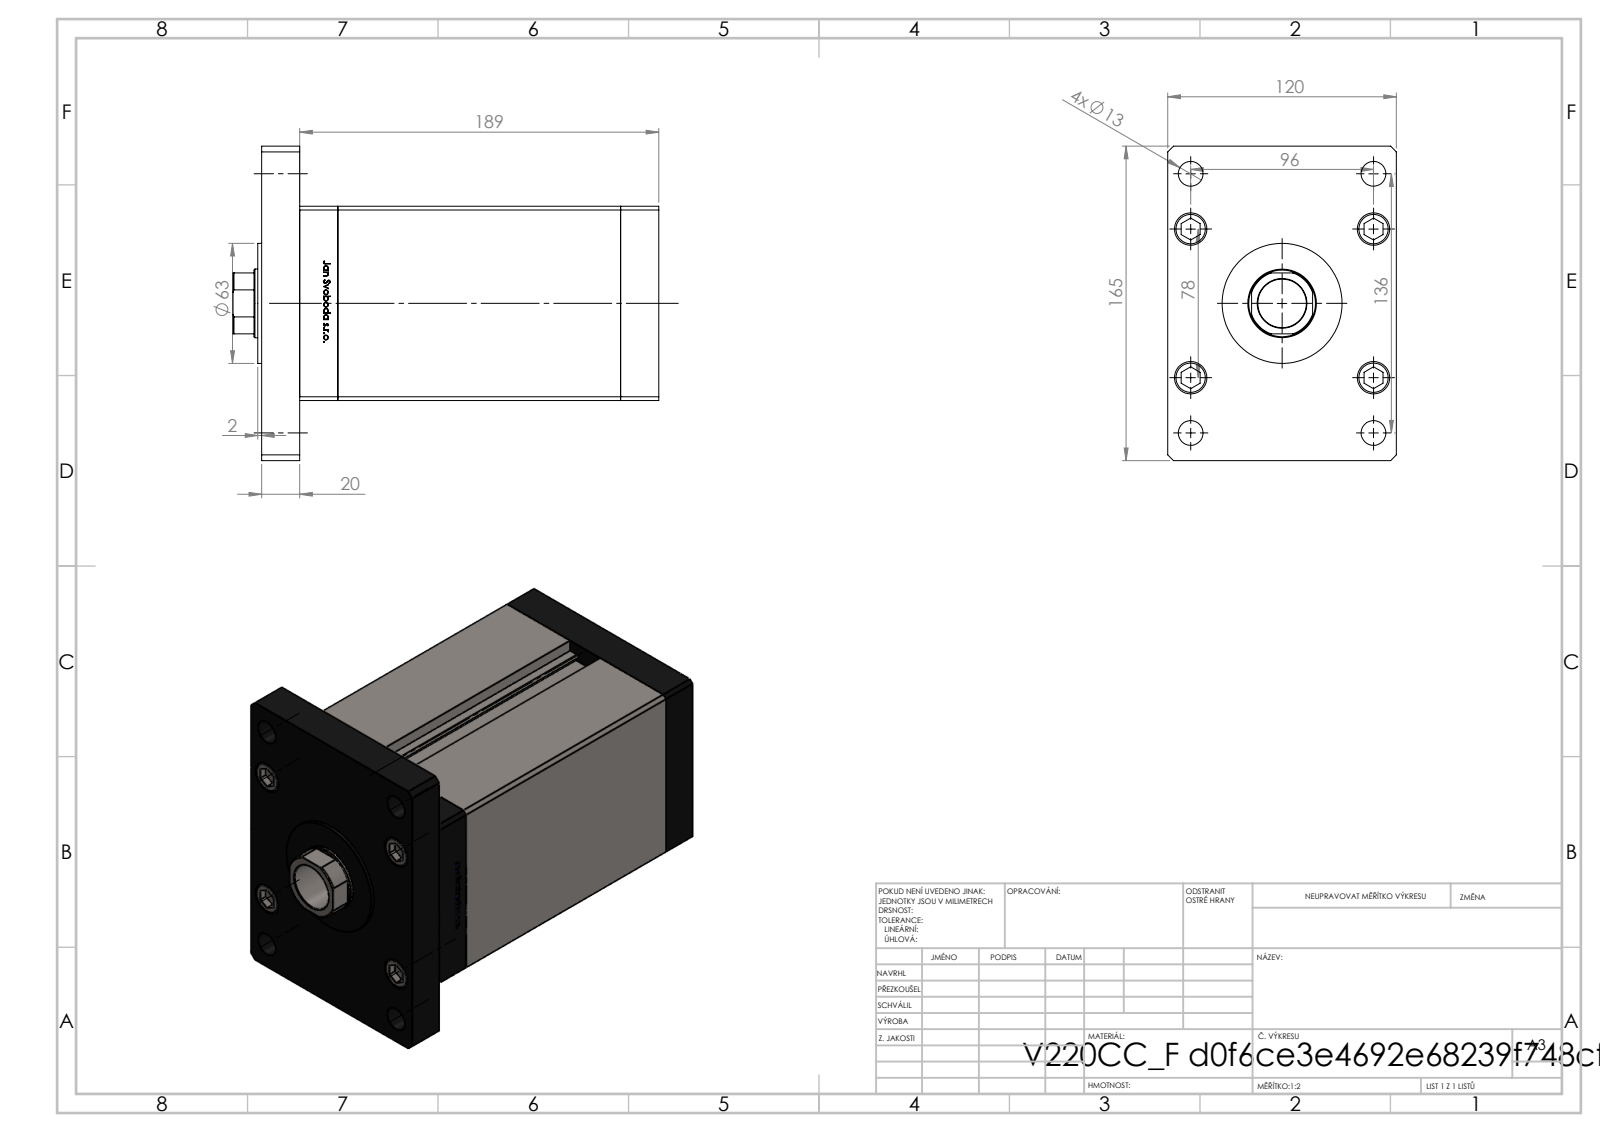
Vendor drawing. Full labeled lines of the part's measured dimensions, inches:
Part name (STEP PRODUCT): V220C_FRONT_F; V220C_F; V220C_F_MIDDLE; V220C BACK_F (+2 more)
STEP written by: SolidWorks 2019 (CONFIG_CONTROL_DESIGN)
Units: inches
Bodies: 19 solids, 1311 faces (517 planar, 188 cylindrical, 606 other)
Overall size (bounding box): 8.799 × 6.496 × 4.724
Volume: 147.5 in³ · Surface area: 498.2 in²
Round holes (diameter × count): ⌀0.531 ×5, ⌀0.709 ×5, ⌀0.472 ×4, ⌀0.512 ×4, ⌀0.669 ×4, ⌀0.079 ×2, ⌀0.518 ×2, ⌀1.004 ×1, ⌀1.417 ×1, ⌀1.476 ×1
Round bosses / shafts (diameter × count): ⌀0.315 ×9, ⌀0.669 ×5, ⌀2.48 ×1
Partial cylindrical surfaces — rounded edges, fillets, slot ends (radius × count): R0.037 ×2, R0.689 ×1
Main face-to-face distances: 0.787, 6.634, 7.421, 4.724, 4.016, 5.846, 1.575, 8.209, 1.348, 1.654
Hole centre spacings: 1.634, 1.142, 2.435, 3.277, 3.78, 3.948, 4.213, 5.659
